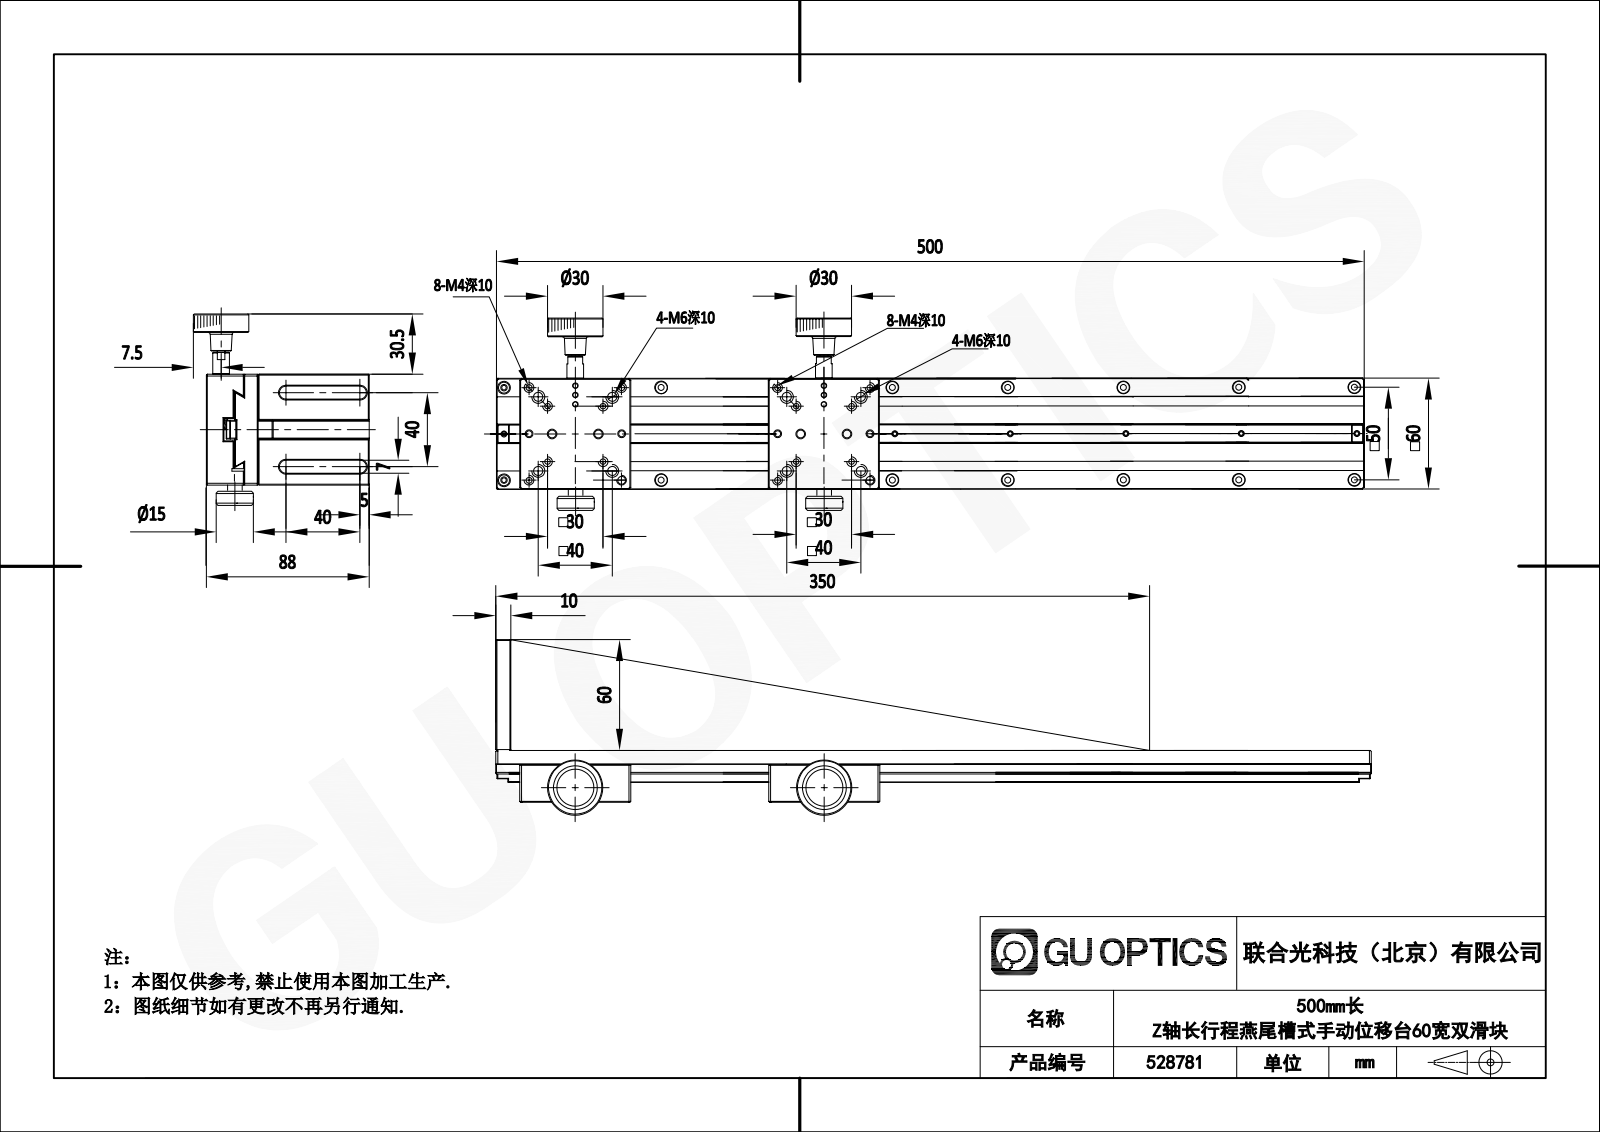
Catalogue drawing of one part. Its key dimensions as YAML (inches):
part_name: "528781"
step_written_by: "SolidWorks 2020 (CONFIG_CONTROL_DESIGN)"
units: inches
bodies: {solids: 50, faces: 1581, planar: 747, cylindrical: 400, other: 434}
overall_size: [20, 4.03, 2.548]
volume: 47.58
surface_area: 350.6
round_holes:
  - {diameter: 0.13, count: 40}
  - {diameter: 0.177, count: 26}
  - {diameter: 0.098, count: 20}
  - {diameter: 0.197, count: 15}
  - {diameter: 0.236, count: 14}
  - {diameter: 0.315, count: 10}
  - {diameter: 0.081, count: 9}
  - {diameter: 0.114, count: 7}
  - {diameter: 0.157, count: 2}
  - {diameter: 0.161, count: 2}
  - {diameter: 0.394, count: 2}
round_bosses_or_shafts:
  - {diameter: 0.118, count: 11}
  - {diameter: 0.098, count: 9}
  - {diameter: 0.177, count: 7}
  - {diameter: 0.354, count: 4}
  - {diameter: 0.157, count: 4}
  - {diameter: 1.181, count: 2}
  - {diameter: 0.394, count: 2}
  - {diameter: 0.315, count: 2}
partial_cylinders:
  - {radius: 0.041, count: 19}
  - {radius: 0.039, count: 6}
  - {radius: 0.008, count: 2}
  - {radius: 0.047, count: 2}
face_to_face_distances: [0.394, 0.874, 0.48, 0.689, 0.295, 0.185, 2.362, 1.417, 0.945, 0.39]
hole_center_spacings: [1.969, 2.953, 3.549, 0.278, 1.392, 1.623, 1.783, 0.71]
